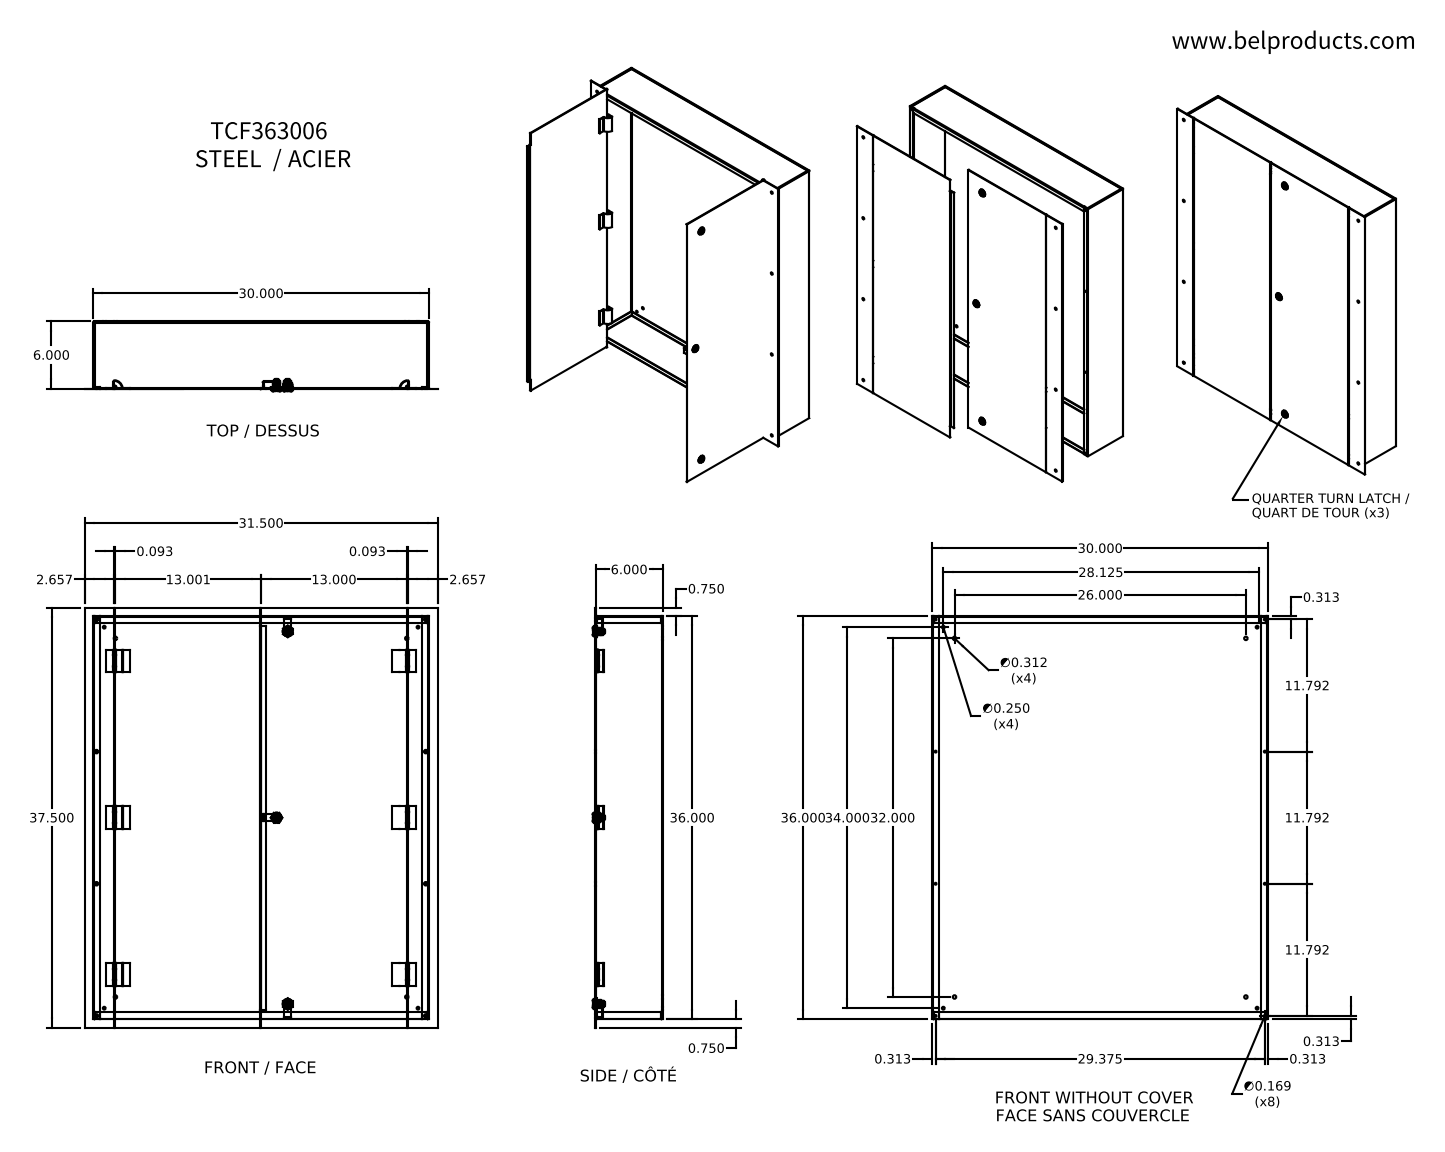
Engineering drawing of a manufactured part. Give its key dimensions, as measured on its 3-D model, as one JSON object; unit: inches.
{"part_name": "LOCK AVEC TOURNEVIS TYPE 4-12 SANS CAME; HOSING-oa0; INSERT POUR TOURNEVIS-oa1; NOIX DE FIXATION-oa2 (+8 more)", "step_written_by": "Unknown (AUTOMOTIVE_DESIGN)", "units": "inches", "bodies": {"solids": 46, "faces": 1693, "planar": 850, "cylindrical": 421, "other": 422}, "overall_size": [37.5, 31.5, 6.251], "volume_in3": 240.8, "surface_area_in2": 6496, "round_holes": [[0.312, 12], [0.169, 8], [0.25, 4], [0.358, 3], [0.44, 3], [0.505, 3], [0.622, 3], [0.687, 3], [0.15, 2], [0.275, 2]], "round_bosses_or_shafts": [[0.9, 3], [0.89, 3], [0.62, 3], [0.51, 3], [0.497, 3], [0.48, 3], [0.467, 3], [0.397, 3]], "partial_cylinders_radius": [[0.375, 34], [0.01, 24], [0.032, 17], [0.107, 14], [0.371, 6], [0.06, 4], [0.12, 4], [0.137, 3]], "face_to_face_distances": [0.075, 6, 5.925, 6.075, 0.075, 29.925, 35.925, 30, 29.85, 36], "hole_center_spacings": [31.653, 0.972, 1.414, 2.386, 10.244, 11.126, 11.792, 21.961]}
